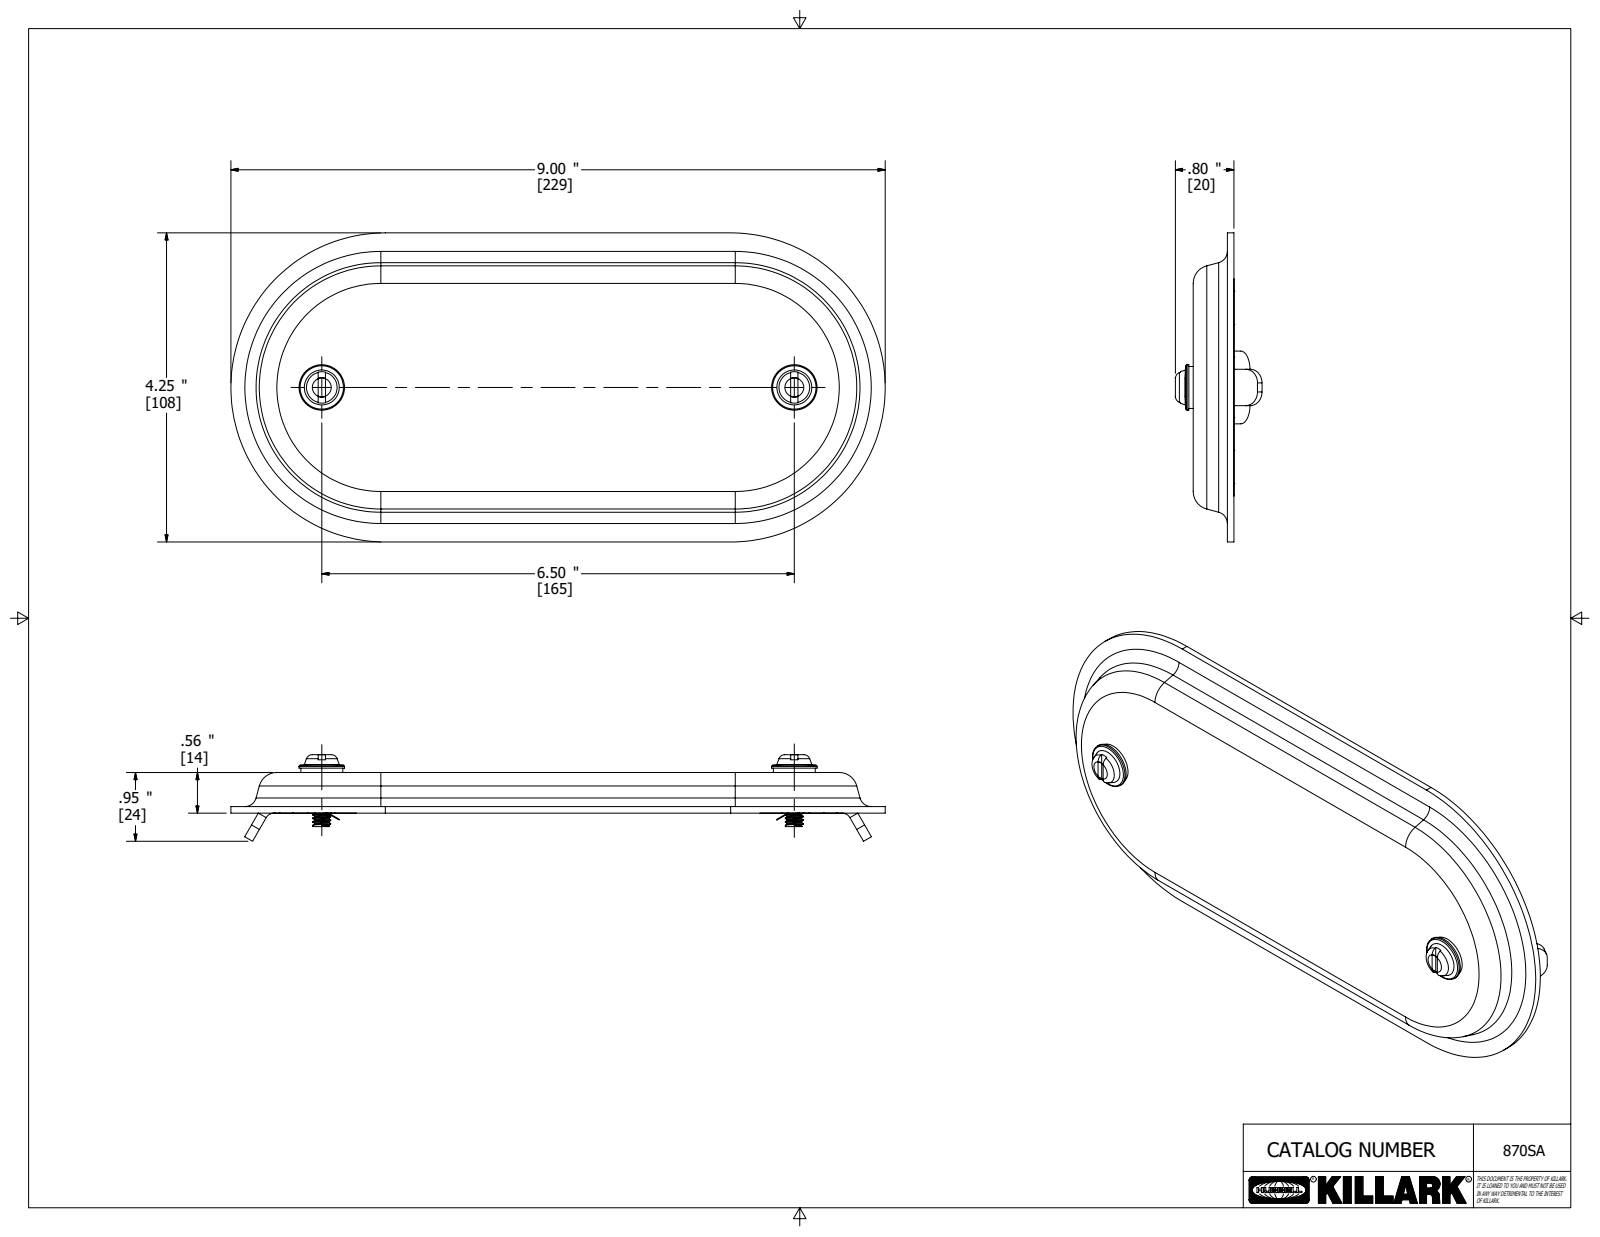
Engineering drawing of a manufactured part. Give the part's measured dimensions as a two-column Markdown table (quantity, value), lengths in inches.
| quantity | value |
| --- | --- |
| part name | 870SA; 17733; 18038CABB; 17953 |
| STEP written by | Autodesk Inventor 2018 (AUTOMOTIVE_DESIGN) |
| units | inches |
| bodies | 5 solids, 156 faces (76 planar, 52 cylindrical, 28 other) |
| overall size | 9 × 4.25 × 1.191 |
| volume | 4.671 in³ |
| surface area | 103.3 in² |
| round holes (diameter × count) | 0.25 × 2, 0.344 × 2 |
| round bosses / shafts (diameter × count) | 0.625 × 2, 0.577 × 2, 0.246 × 2, 0.196 × 2 |
| partial cylindrical surfaces (radius × count) | 0.187 × 8, 0.25 × 8, 0.125 × 4, 0.16 × 4, 0.5 × 4, 0.875 × 4, 0.219 × 2, 2.125 × 2 |
| main face-to-face distances | 0.09, 0.469, 0.559, 0.125, 0.09, 0.379, 0.469, 0.035, 0.344, 0.434 |
| hole center spacings | 6.5, 6.5, 6.5 |
